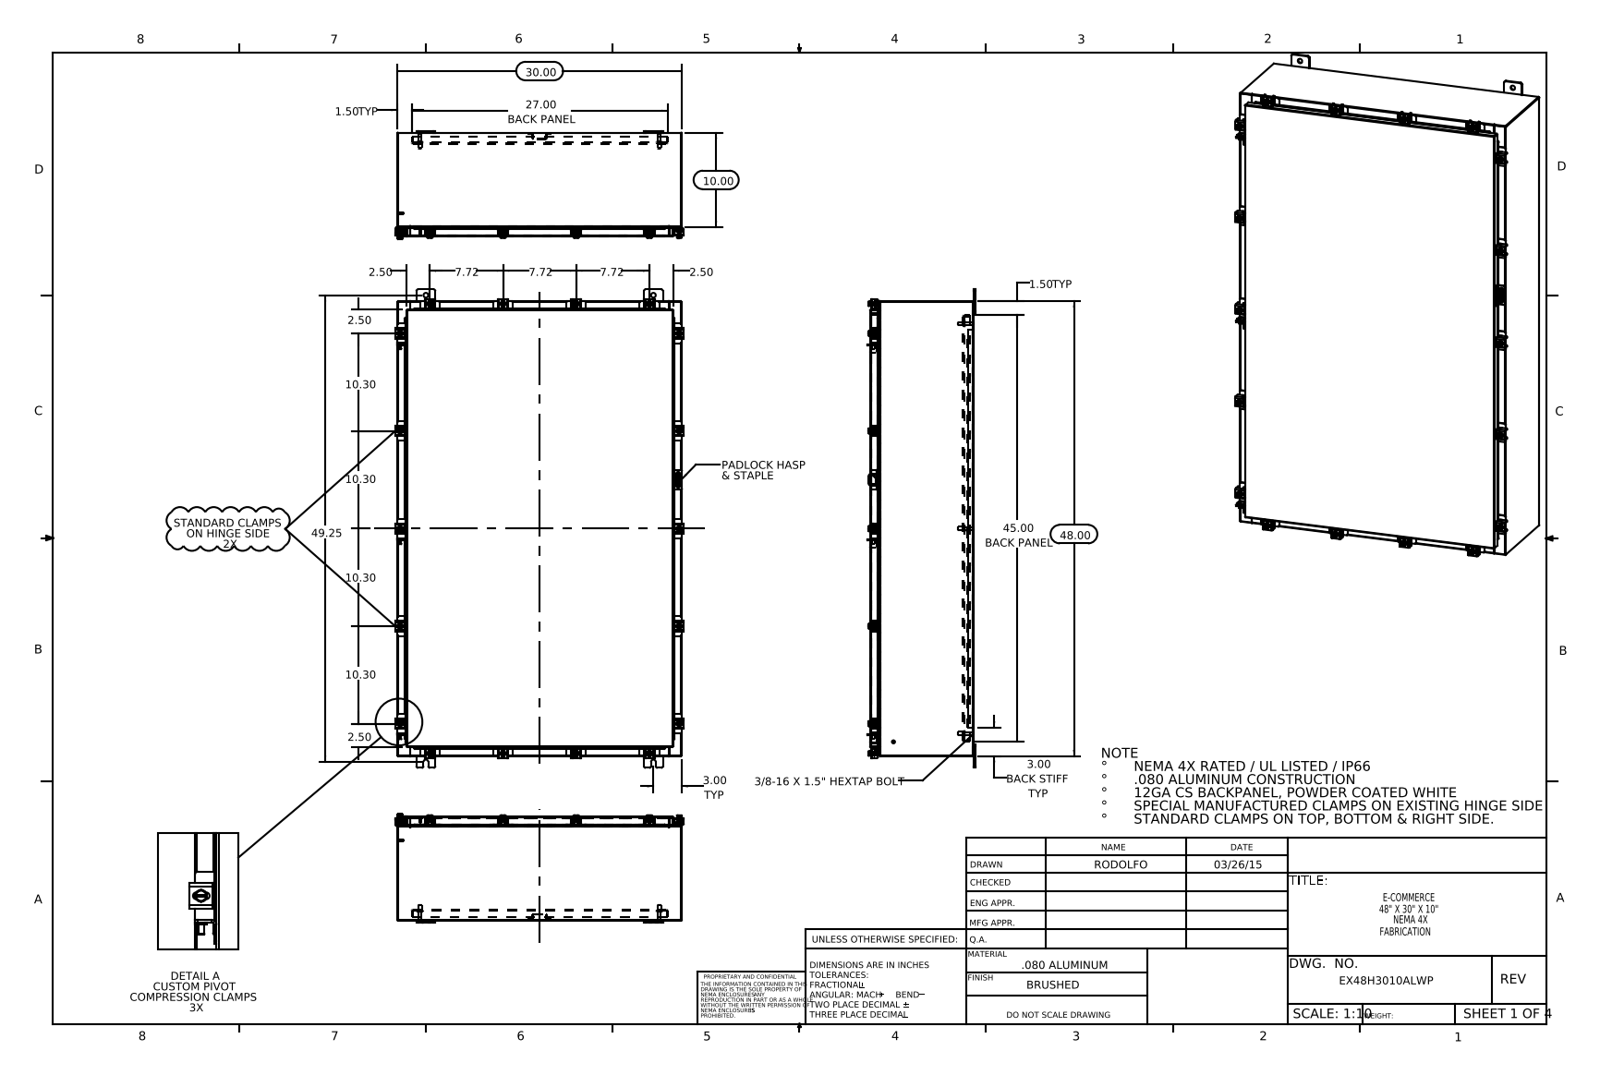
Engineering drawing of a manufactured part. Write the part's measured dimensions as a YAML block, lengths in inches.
part_name: "EX48H3010ALWP; EX48H3010ALWP Cover; EX48H3010ALWP Standard Clamps; EX48H3010ALWP Body (+8 more)"
step_written_by: "SolidWorks 2014 (AUTOMOTIVE_DESIGN)"
units: inches
bodies: {solids: 116, faces: 2878, planar: 1525, cylindrical: 1123, other: 230}
overall_size: [50.5, 30.421, 11.453]
volume: 516.4
surface_area: 12799
round_holes:
  - {diameter: 0.213, count: 18}
  - {diameter: 0.26, count: 18}
  - {diameter: 0.5, count: 10}
  - {diameter: 0.125, count: 1}
  - {diameter: 0.25, count: 1}
round_bosses_or_shafts:
  - {diameter: 0.5, count: 18}
  - {diameter: 0.25, count: 18}
  - {diameter: 0.399, count: 15}
  - {diameter: 0.625, count: 6}
  - {diameter: 0.375, count: 6}
  - {diameter: 0.33, count: 6}
  - {diameter: 0.315, count: 2}
  - {diameter: 0.236, count: 2}
partial_cylinders:
  - {radius: 0.06, count: 76}
  - {radius: 0.141, count: 36}
  - {radius: 0.12, count: 33}
  - {radius: 0.013, count: 30}
  - {radius: 0.09, count: 27}
  - {radius: 0.088, count: 26}
  - {radius: 0.05, count: 25}
  - {radius: 0.145, count: 24}
face_to_face_distances: [0.075, 10.9, 10.826, 10.975, 0.104, 1, 1.075, 9.826, 9.9, 1.179]
hole_center_spacings: [31.2, 29.451, 2.347, 4.44, 10.298, 20.701, 21.625, 23.749]
